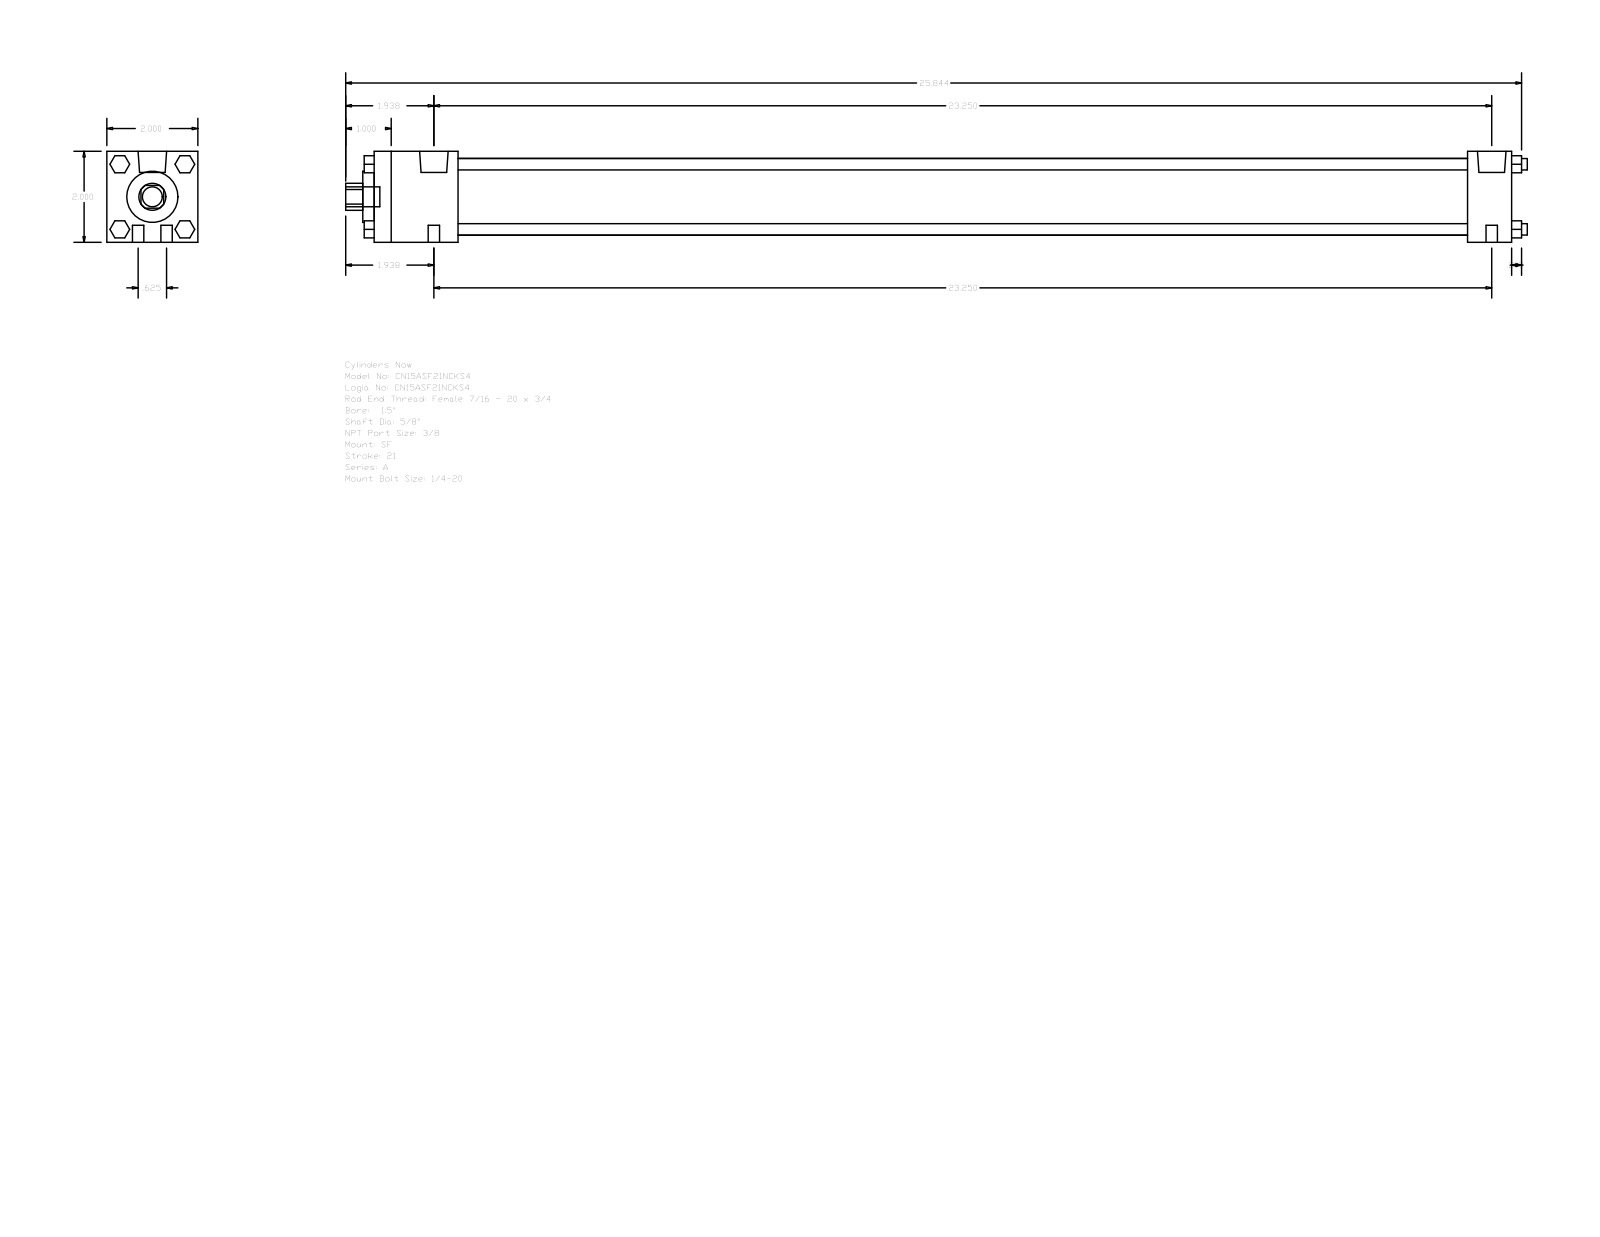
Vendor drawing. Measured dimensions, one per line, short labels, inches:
name: A_SF__0150_0.625
written by: GSSL Pune (CONFIG_CONTROL_DESIGN)
unit: in
bodies: 0 solids, 124 faces (94 planar, 30 cylindrical, 0 other)
size: 25.969 × 2 × 2
holes: 1× ⌀0.625, 1× ⌀1.125, 1× ⌀1.69
bosses: 8× ⌀0.25, 2× ⌀0.627, 2× ⌀0.219, 1× ⌀0.437
rounds: 1× R0.297
face distances: 2, 25, 1.844, 24.031, 22.187, 23.156, 0.969, 0.375, 0.25, 2.094
